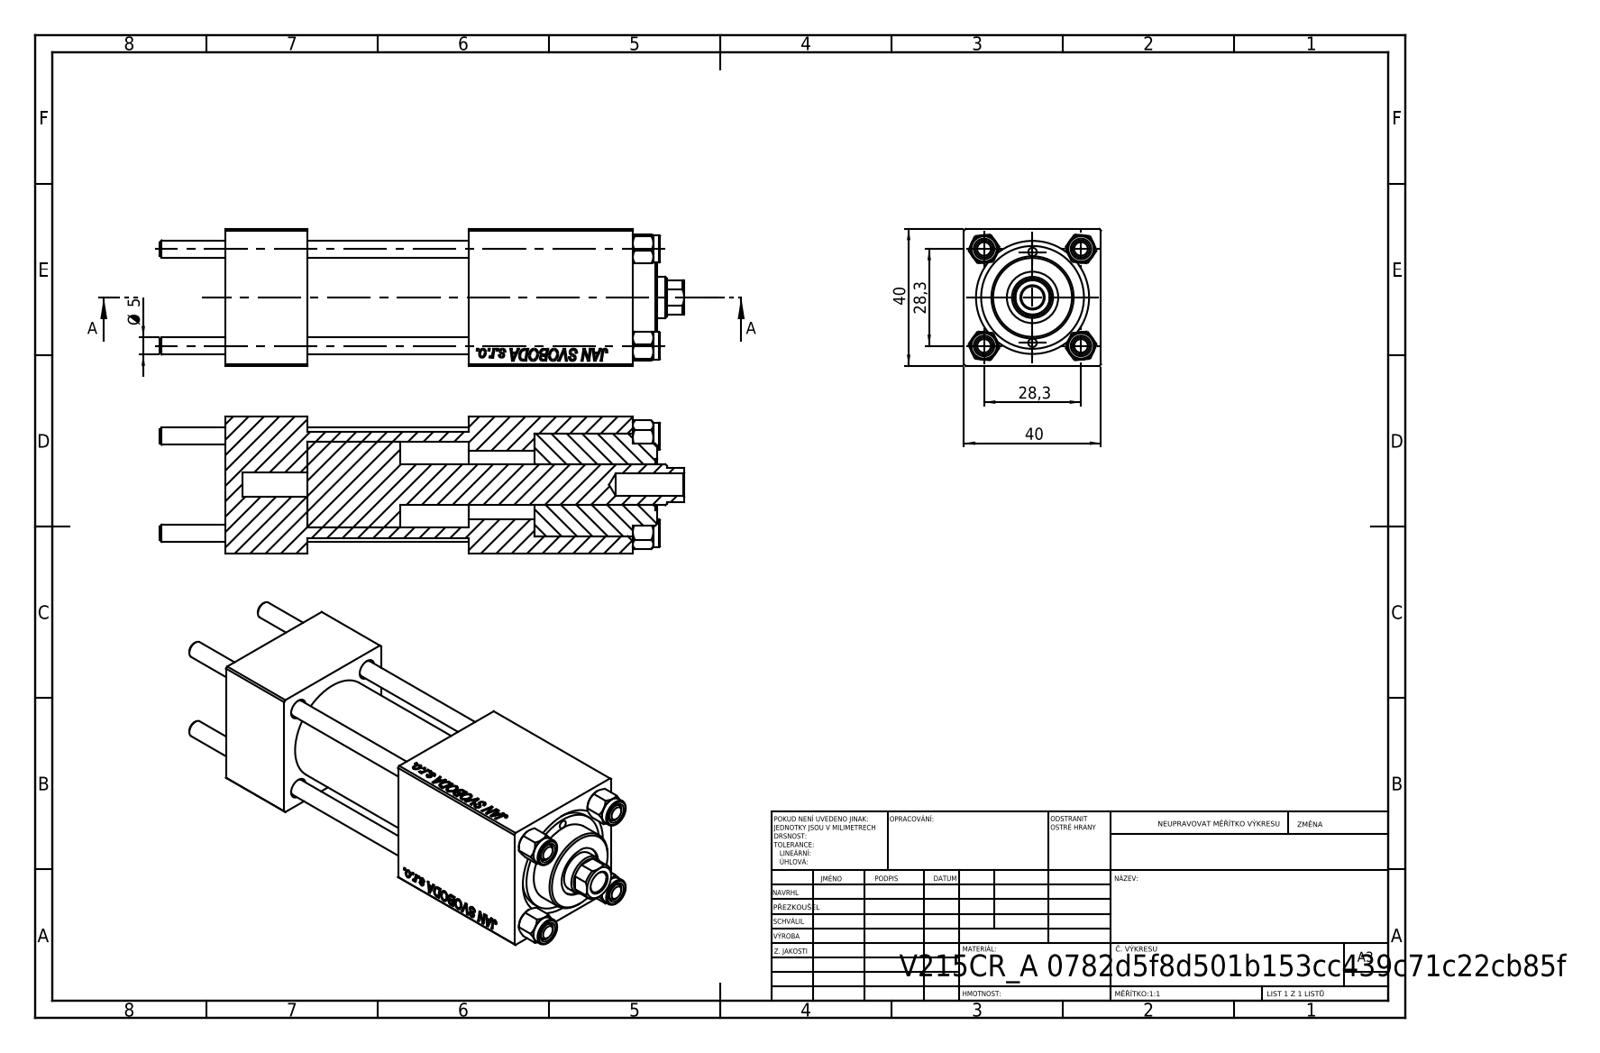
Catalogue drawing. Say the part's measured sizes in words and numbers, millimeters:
The part is named "CR025_012_A_0_G_A_G_M_020_+#_##_TYCINKA; V215CR_VCP; V215_VC_A; NUT_M5 (+1 more)". Its 3-D file was written by "SolidWorks 2019 (CONFIG_CONTROL_DESIGN)". It is 11 solids with 1137 faces: 519 planar, 82 cylindrical and 536 other. Overall it measures 153 by 40 by 40 millimeters. Its volume is 144 775 cubic millimeters and its surface area 58 950 square millimeters. Round holes: 4 of diameter 5, 3 of diameter 20, 2 of diameter 2.5, 2 of diameter 7, 2 of diameter 13.16, 1 of diameter 6.5, 1 of diameter 12, 1 of diameter 15, 1 of diameter 25, 1 of diameter 30. Round bosses or shafts: 4 of diameter 8, 1 of diameter 31, 1 of diameter 24. Partial cylindrical surfaces (rounded edges, fillets, slot ends): 1 of radius 5.5. The main face-to-face distances are 40, 24, 90.3, 66.3, 119, 95, 28.7, 71, 47, 19.3. The hole center spacings are 14.18, 20.01, 28.3, 30.84, 13.25, 40.02, 26.5, 72.
